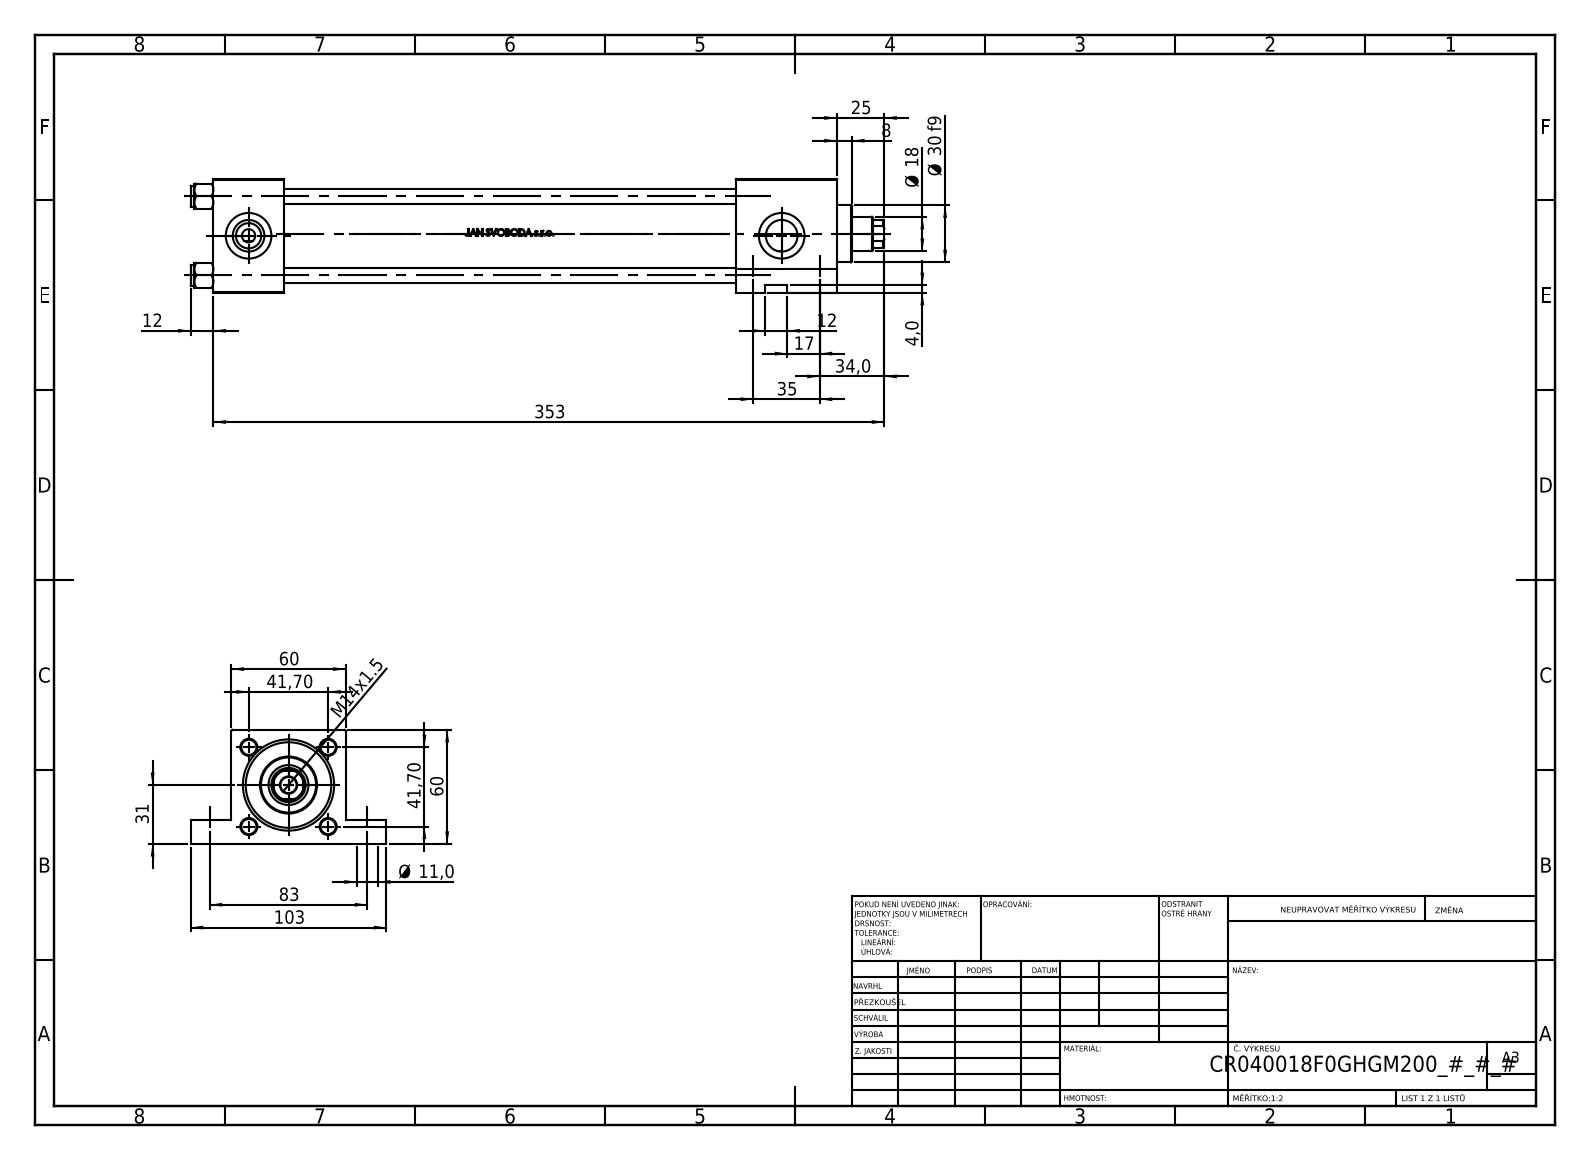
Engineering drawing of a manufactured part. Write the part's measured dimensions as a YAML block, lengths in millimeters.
part_name: "NUT_M5_F; V215CR_F_TYCINKA; V215CR_F_Body; V215CR_VCP_F (+1 more)"
step_written_by: "SolidWorks 2019 (CONFIG_CONTROL_DESIGN)"
units: millimeters
bodies: {solids: 11, faces: 1118, planar: 437, cylindrical: 141, other: 540}
overall_size: [365, 103, 60]
volume: 578575
surface_area: 188443
round_holes:
  - {diameter: 8, count: 4}
  - {diameter: 11, count: 4}
  - {diameter: 7, count: 2}
  - {diameter: 16.66, count: 2}
  - {diameter: 24, count: 2}
  - {diameter: 8.5, count: 1}
  - {diameter: 18, count: 1}
  - {diameter: 21, count: 1}
  - {diameter: 31, count: 1}
  - {diameter: 40, count: 1}
  - {diameter: 45, count: 1}
round_bosses_or_shafts:
  - {diameter: 11, count: 4}
  - {diameter: 46, count: 1}
  - {diameter: 30, count: 1}
partial_cylinders:
  - {radius: 8.5, count: 1}
face_to_face_distances: [60, 37, 328, 291, 275, 238, 53, 299.3, 262.3, 24.3]
hole_center_spacings: [41.7, 28.79, 30.2, 35, 58.97, 83, 90.08, 280.5]
